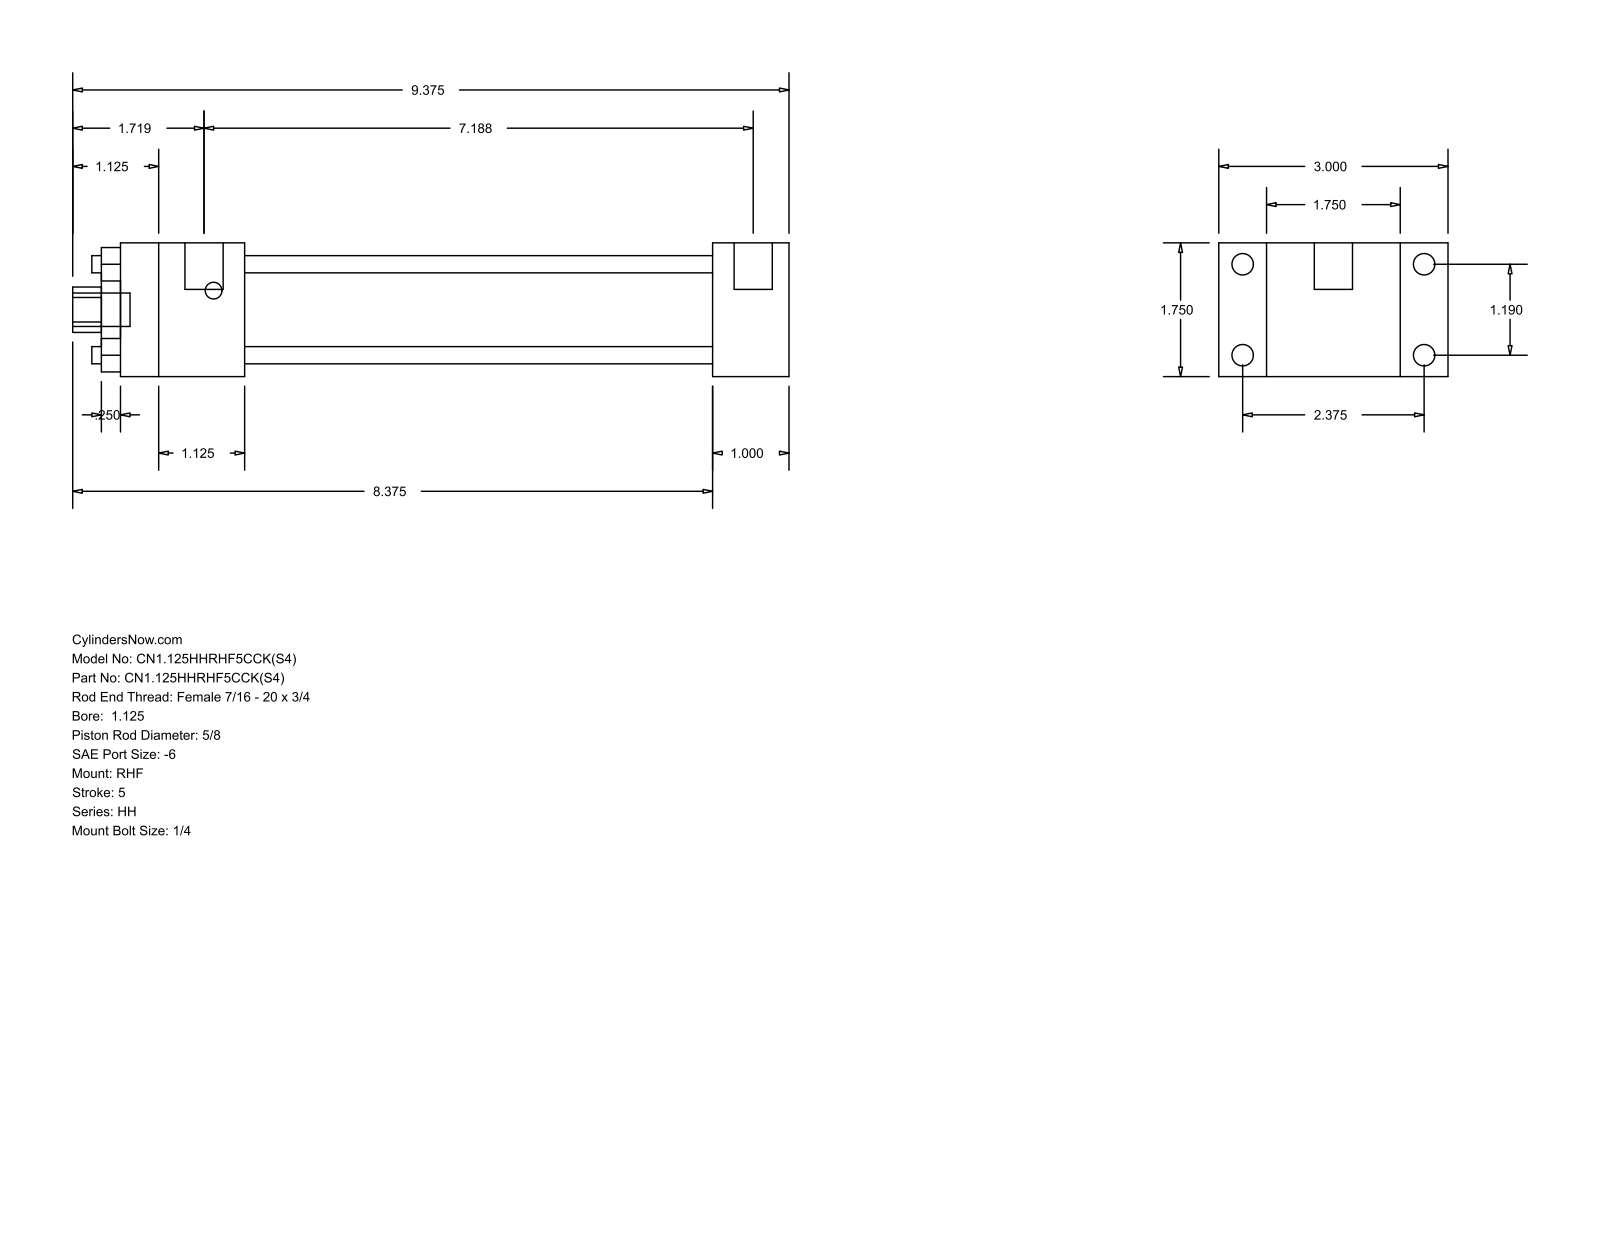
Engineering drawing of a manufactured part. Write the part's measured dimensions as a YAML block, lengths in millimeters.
part_name: "HH_RHF__0112_0.625"
step_written_by: "GSSL Pune (CONFIG_CONTROL_DESIGN)"
units: millimeters
bodies: {solids: 0, faces: 88, planar: 60, cylindrical: 28, other: 0}
overall_size: [238.12, 76.2, 44.45]
round_holes:
  - {diameter: 5.71, count: 4}
  - {diameter: 15.88, count: 1}
  - {diameter: 28.57, count: 1}
  - {diameter: 34.92, count: 1}
round_bosses_or_shafts:
  - {diameter: 7.14, count: 4}
  - {diameter: 5.56, count: 4}
  - {diameter: 12.7, count: 2}
  - {diameter: 11.11, count: 1}
partial_cylinders:
  - {radius: 7.54, count: 1}
face_to_face_distances: [44.46, 15.87, 60.33, 25.4, 76.2, 155.57, 180.97, 41.27, 196.84, 222.24]
hole_center_spacings: [21.37, 30.22, 42.74]
